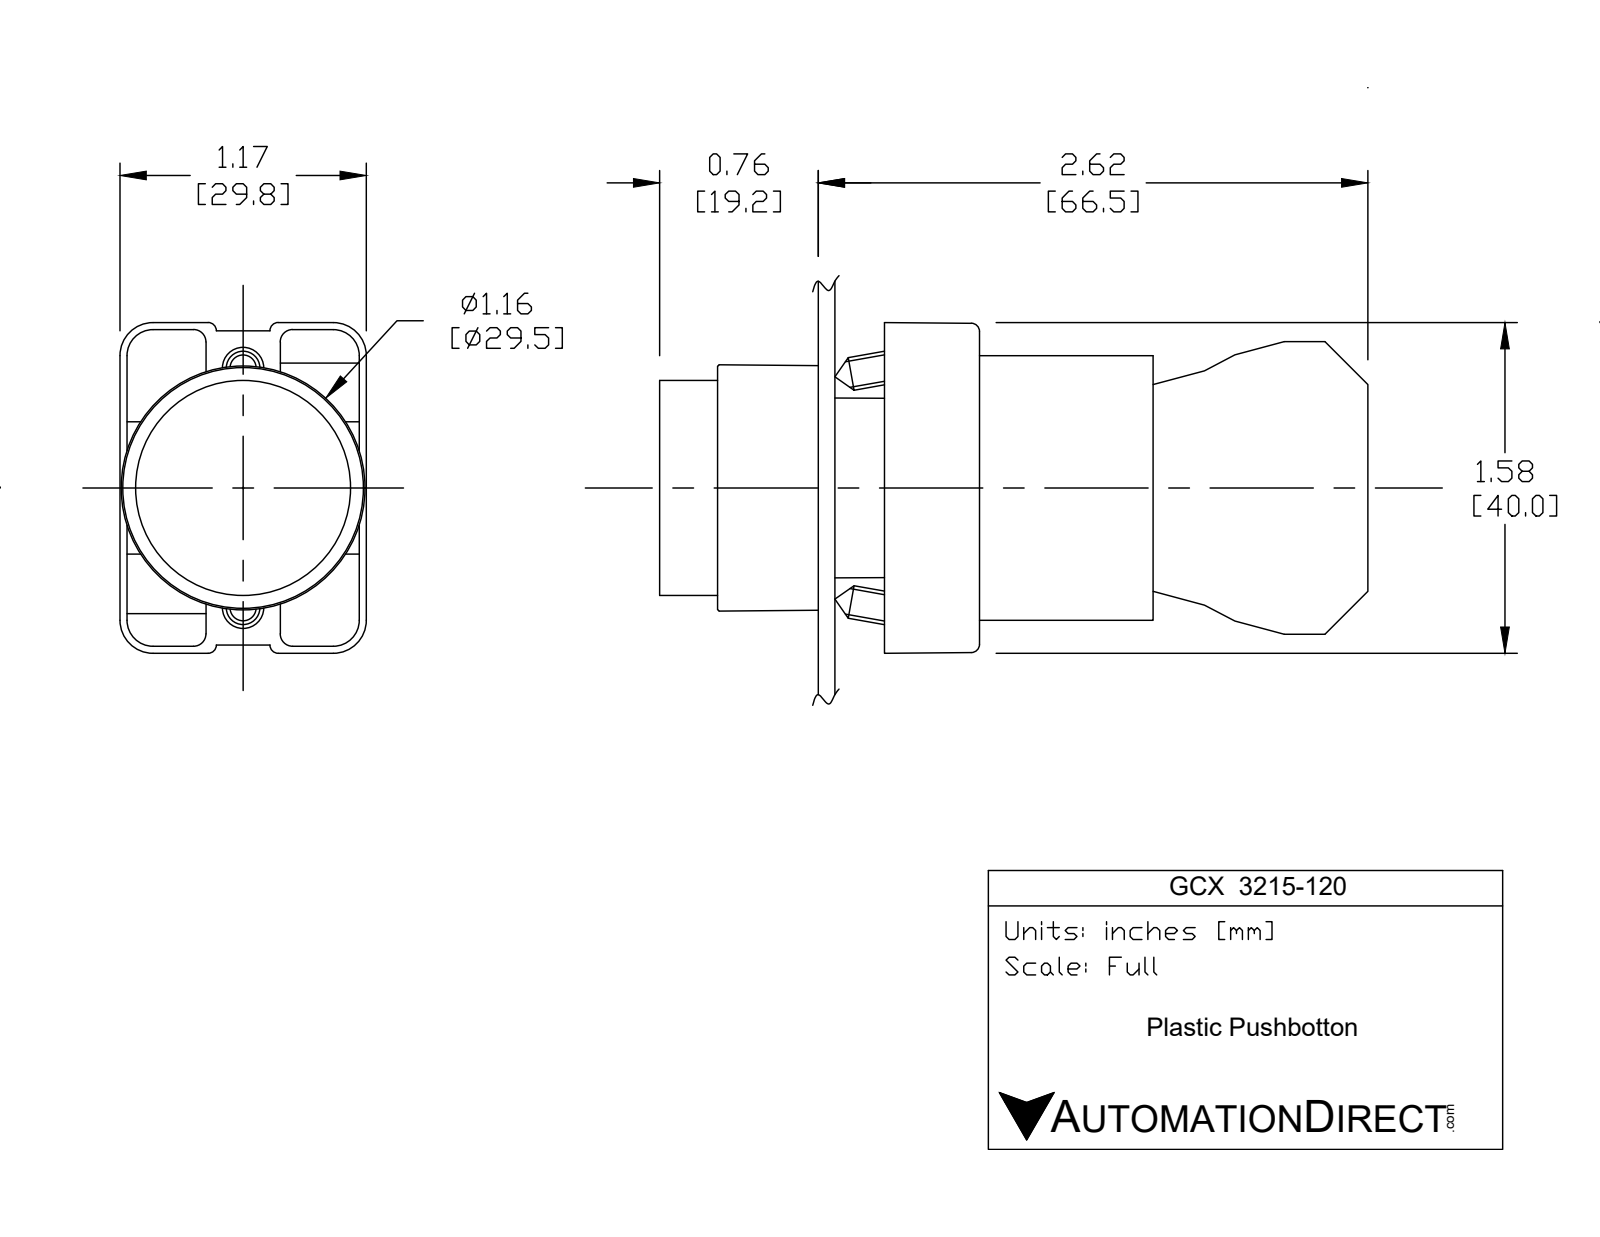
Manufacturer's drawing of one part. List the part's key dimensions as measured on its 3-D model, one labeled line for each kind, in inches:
Part name (STEP PRODUCT): ecx1040; GCX3215-120; ECX3029-2; GCX3215 OPERATOR (+1 more)
STEP written by: SolidWorks 2016 (AUTOMOTIVE_DESIGN)
Units: inches
Bodies: 7 solids, 425 faces (250 planar, 144 cylindrical, 31 other)
Overall size (bounding box): 3.319 × 1.581 × 1.177
Volume: 2.721 in³ · Surface area: 36.32 in²
Round holes (diameter × count): ⌀0.079 ×2, ⌀0.124 ×2, ⌀0.13 ×2, ⌀0.087 ×1, ⌀0.197 ×1, ⌀0.469 ×1, ⌀0.878 ×1, ⌀0.888 ×1, ⌀1.024 ×1
Round bosses / shafts (diameter × count): ⌀0.157 ×4, ⌀1.175 ×1, ⌀1.004 ×1, ⌀0.945 ×1, ⌀0.856 ×1, ⌀0.78 ×1, ⌀0.504 ×1
Partial cylindrical surfaces — rounded edges, fillets, slot ends (radius × count): R0.059 ×24, R0.041 ×12, R0.124 ×12, R0.157 ×12, R0.039 ×8, R0.128 ×2, R0.02 ×1, R0.063 ×1
Main face-to-face distances: 0.827, 0.579, 1.171, 2.02, 1.193, 0.031, 0.033, 0.573, 1.165, 0.593
Hole centre spacings: 0.236, 0.544, 0.472, 0.49
